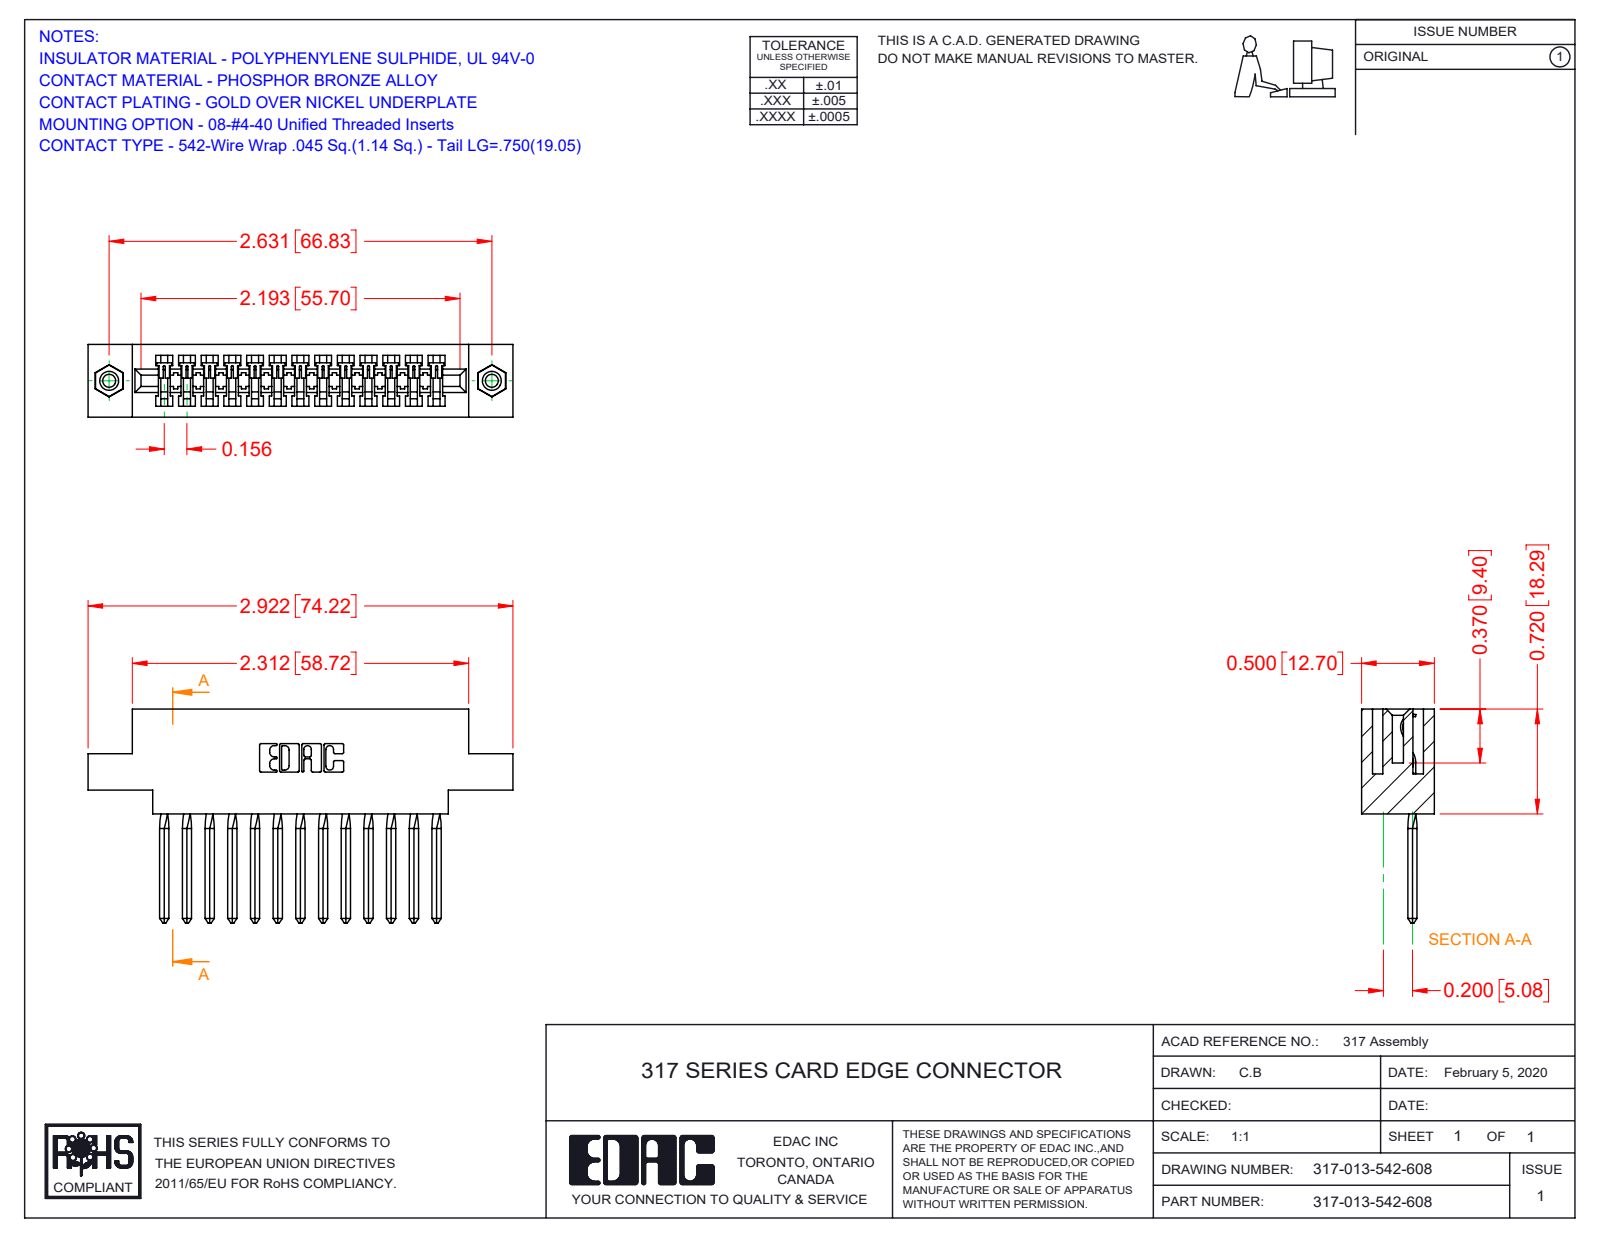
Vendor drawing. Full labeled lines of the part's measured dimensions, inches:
Part name (STEP PRODUCT): 345-250-001_345-250-003-102; 317 Part_.156 Dia - TI; 317-013-542-678; 317-290-003_542
STEP written by: SolidWorks 2016 (CONFIG_CONTROL_DESIGN)
Units: inches
Bodies: 16 solids, 1137 faces (922 planar, 147 cylindrical, 68 other)
Overall size (bounding box): 2.922 × 1.47 × 0.5
Volume: 0.652 in³ · Surface area: 19.24 in²
Round holes (diameter × count): ⌀0.089 ×2, ⌀0.125 ×2, ⌀0.156 ×2
Round bosses / shafts (diameter × count): ⌀0.155 ×2
Partial cylindrical surfaces — rounded edges, fillets, slot ends (radius × count): R0.006 ×26, R0.01 ×22, R0.007 ×6, R0.031 ×6, R0.026 ×3, R0.074 ×1, R0.089 ×1, R0.1 ×1
Main face-to-face distances: 0.5, 0.075, 0.425, 0.11, 0.065, 0.35, 0.22, 0.136, 0.72, 0.331
Hole centre spacings: 2.631
